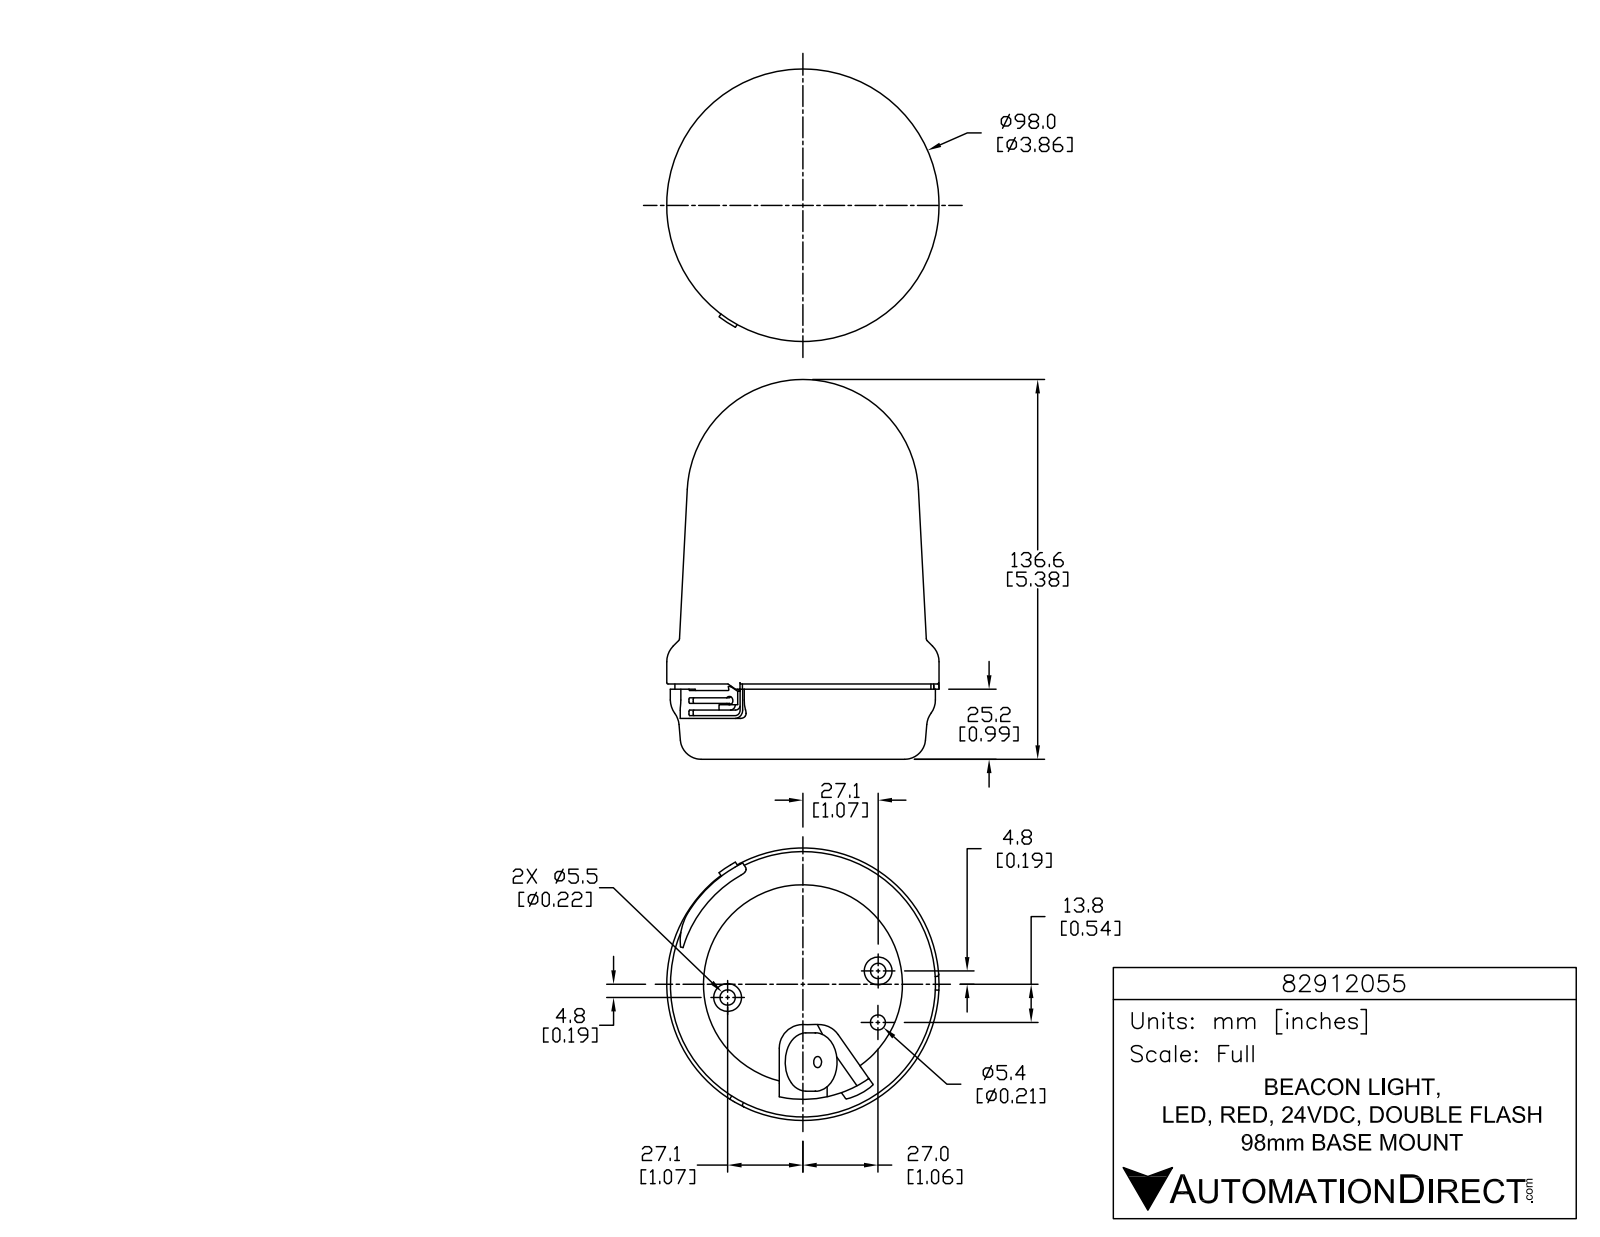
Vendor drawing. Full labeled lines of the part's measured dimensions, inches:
Part name (STEP PRODUCT): 82912055
STEP written by: SolidWorks 2015 (AUTOMOTIVE_DESIGN)
Units: inches
Bodies: 1 solid, 872 faces (566 planar, 204 cylindrical, 102 other)
Overall size (bounding box): 5.378 × 3.858 × 3.858
Volume: 44.69 in³ · Surface area: 73.66 in²
Round holes (diameter × count): ⌀0.059 ×3, ⌀0.217 ×2, ⌀0.157 ×1, ⌀0.213 ×1, ⌀2.819 ×1
Round bosses / shafts (diameter × count): ⌀0.339 ×3, ⌀0.084 ×3, ⌀0.394 ×2, ⌀3.858 ×1, ⌀3.756 ×1, ⌀3.626 ×1, ⌀0.827 ×1
Partial cylindrical surfaces — rounded edges, fillets, slot ends (radius × count): R0.005 ×9, R0.005 ×6, R0.012 ×6, R0.012 ×6, R0.012 ×6, R0.196 ×6, R0.02 ×5, R0.039 ×4
Main face-to-face distances: 1.045, 0.972, 0.073, 0.02, 0.992, 1.065, 0.236, 0.579, 0.559, 0.413
Hole centre spacings: 1.083, 0.73, 1.193, 2.158, 2.165
